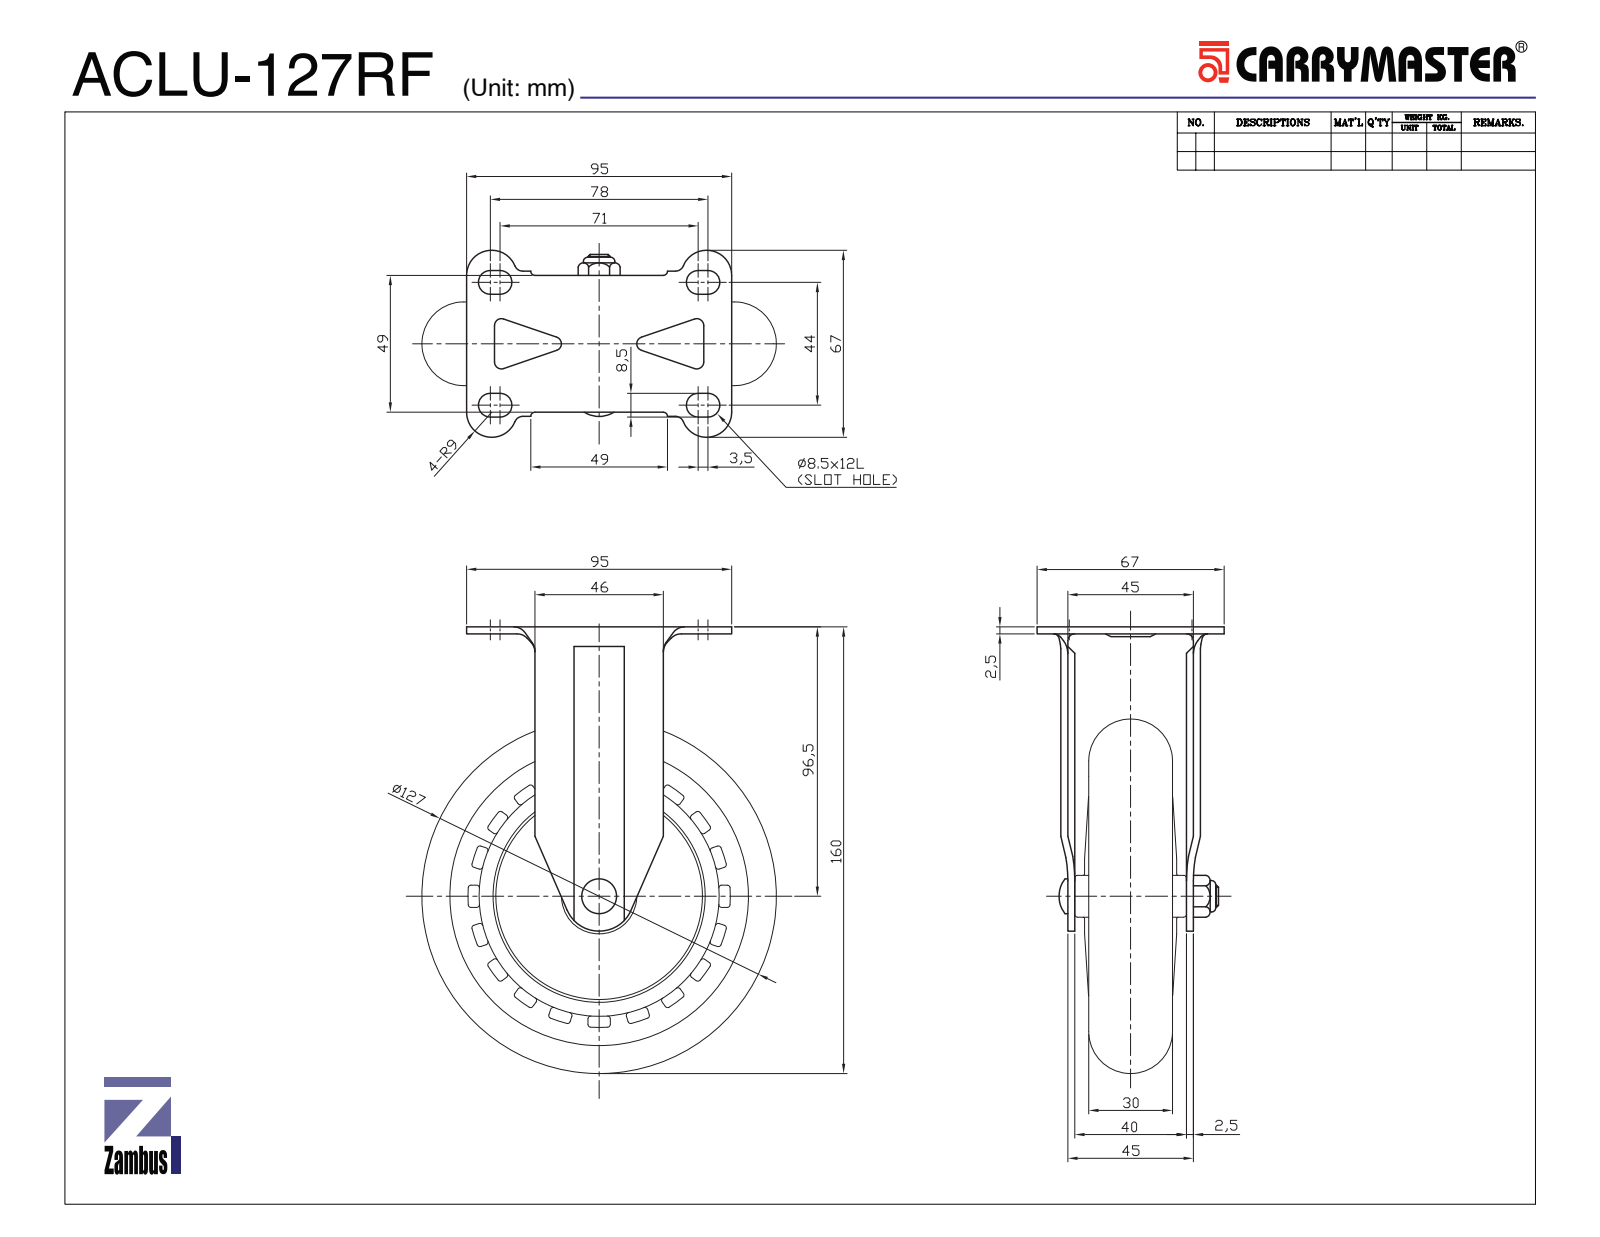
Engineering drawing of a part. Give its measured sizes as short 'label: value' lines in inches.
name: ACLU-127RF; ACLU-127 WHEEL assy; ACLU-127RF FRAME
written by: SolidWorks 2018 (CONFIG_CONTROL_DESIGN)
unit: in
bodies: 6 solids, 831 faces (399 planar, 229 cylindrical, 203 other)
size: 6.326 × 4.921 × 2.559
volume: 18.62 in³; area: 189.2 in²
holes: 1× ⌀0.268, 1× ⌀0.315, 1× ⌀0.378, 1× ⌀0.772, 1× ⌀0.866, 1× ⌀2.795, 1× ⌀2.953, 1× ⌀3.346
bosses: 1× ⌀4.252, 1× ⌀2.874, 1× ⌀1.22, 1× ⌀0.63, 1× ⌀0.512
rounds: 80× R0.039, 16× R0.157, 16× R0.984, 6× R0.079, 4× R0.197, 4× R0.236, 1× R0.512, 1× R1.846
face distances: 0.098, 0.059, 1.201, 0.217, 1.772, 0.197, 0.484, 0.736, 0.256, 0.02
